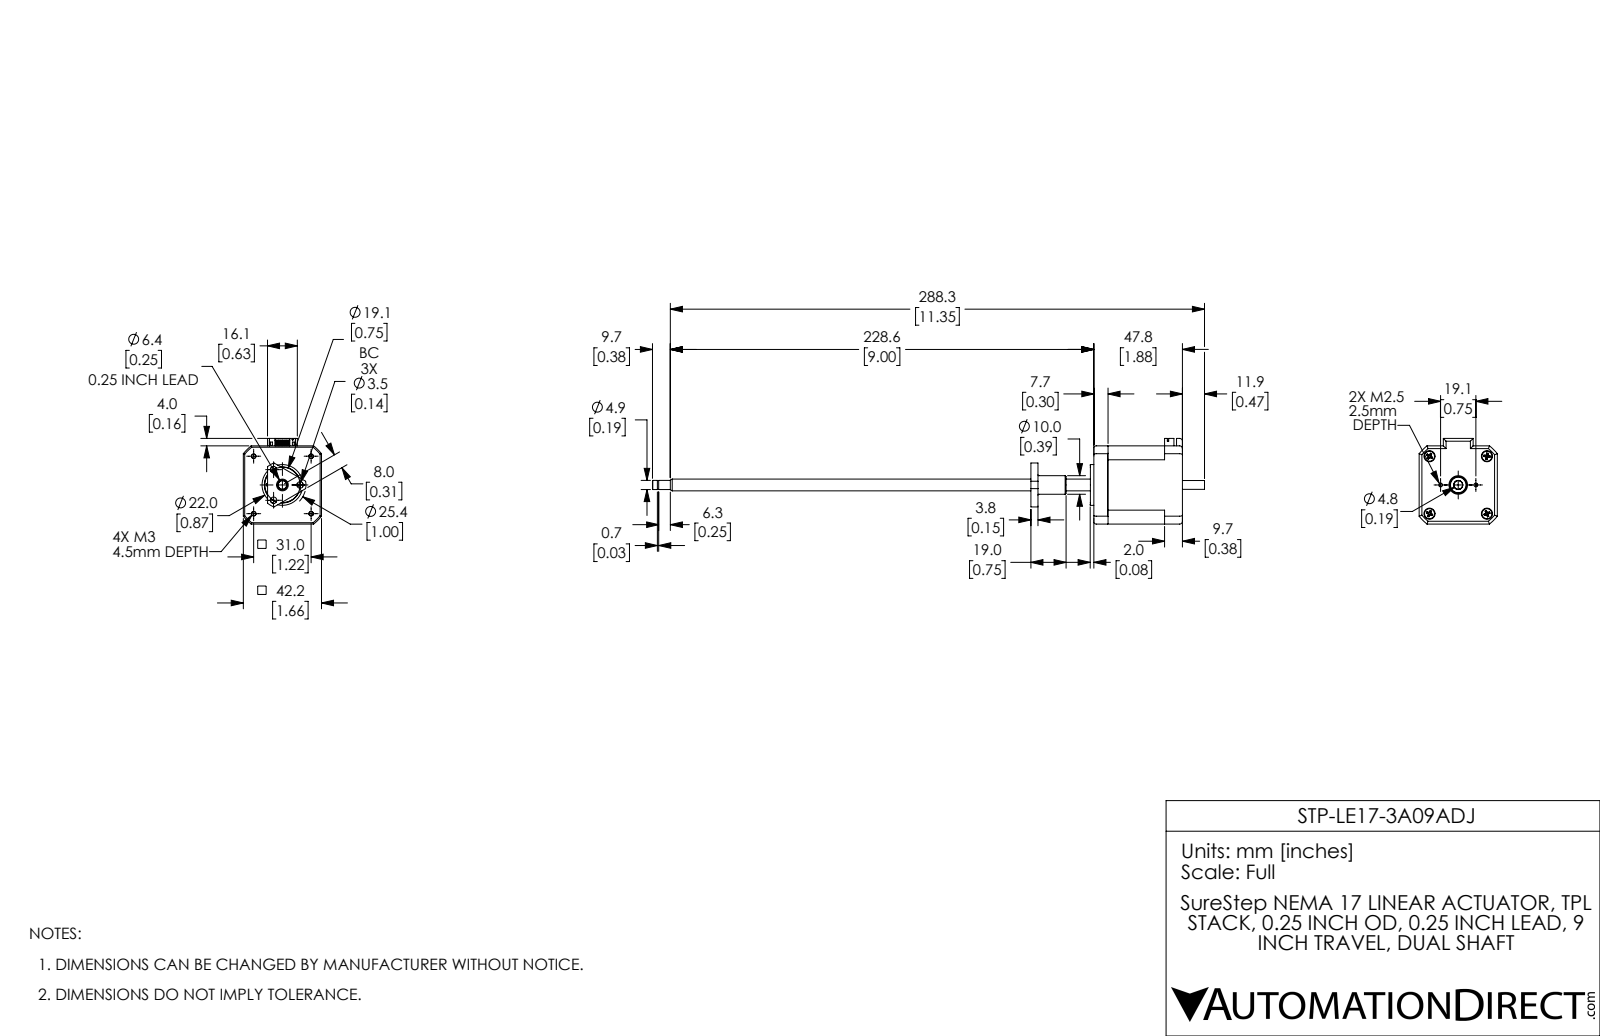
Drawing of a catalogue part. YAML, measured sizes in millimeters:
part_name: "STP-LE17-3A09ADJ; STP-LE17-3A09ADJ_1; STP-LE17-3A09ADJ_2"
step_written_by: "SolidWorks 2017 (AUTOMOTIVE_DESIGN)"
units: millimeters
bodies: {solids: 5, faces: 745, planar: 367, cylindrical: 244, other: 134}
overall_size: [297.95, 46.2, 42.2]
volume: 80948
surface_area: 30233
round_holes:
  - {diameter: 2.5, count: 4}
  - {diameter: 3.8, count: 4}
  - {diameter: 6, count: 4}
  - {diameter: 3.5, count: 3}
  - {diameter: 1.5, count: 2}
  - {diameter: 2.05, count: 2}
  - {diameter: 4.9, count: 1}
  - {diameter: 13, count: 1}
  - {diameter: 17, count: 1}
  - {diameter: 19.46, count: 1}
  - {diameter: 20, count: 1}
round_bosses_or_shafts:
  - {diameter: 5.4, count: 4}
  - {diameter: 2.91, count: 4}
  - {diameter: 27, count: 1}
  - {diameter: 25.91, count: 1}
  - {diameter: 22, count: 1}
  - {diameter: 12, count: 1}
  - {diameter: 10, count: 1}
  - {diameter: 9, count: 1}
partial_cylinders:
  - {radius: 1, count: 12}
  - {radius: 1.5, count: 11}
  - {radius: 2.5, count: 2}
  - {radius: 0.7, count: 1}
  - {radius: 12.7, count: 1}
  - {radius: 14.25, count: 1}
  - {radius: 16, count: 1}
  - {radius: 25.1, count: 1}
face_to_face_distances: [42.2, 9.65, 47.8, 40.15, 38.15, 1.6, 30.5, 7.65, 45.3, 40.6]
hole_center_spacings: [16.61, 9.52, 21.92, 29.43, 31, 4.93, 8, 12.96]
